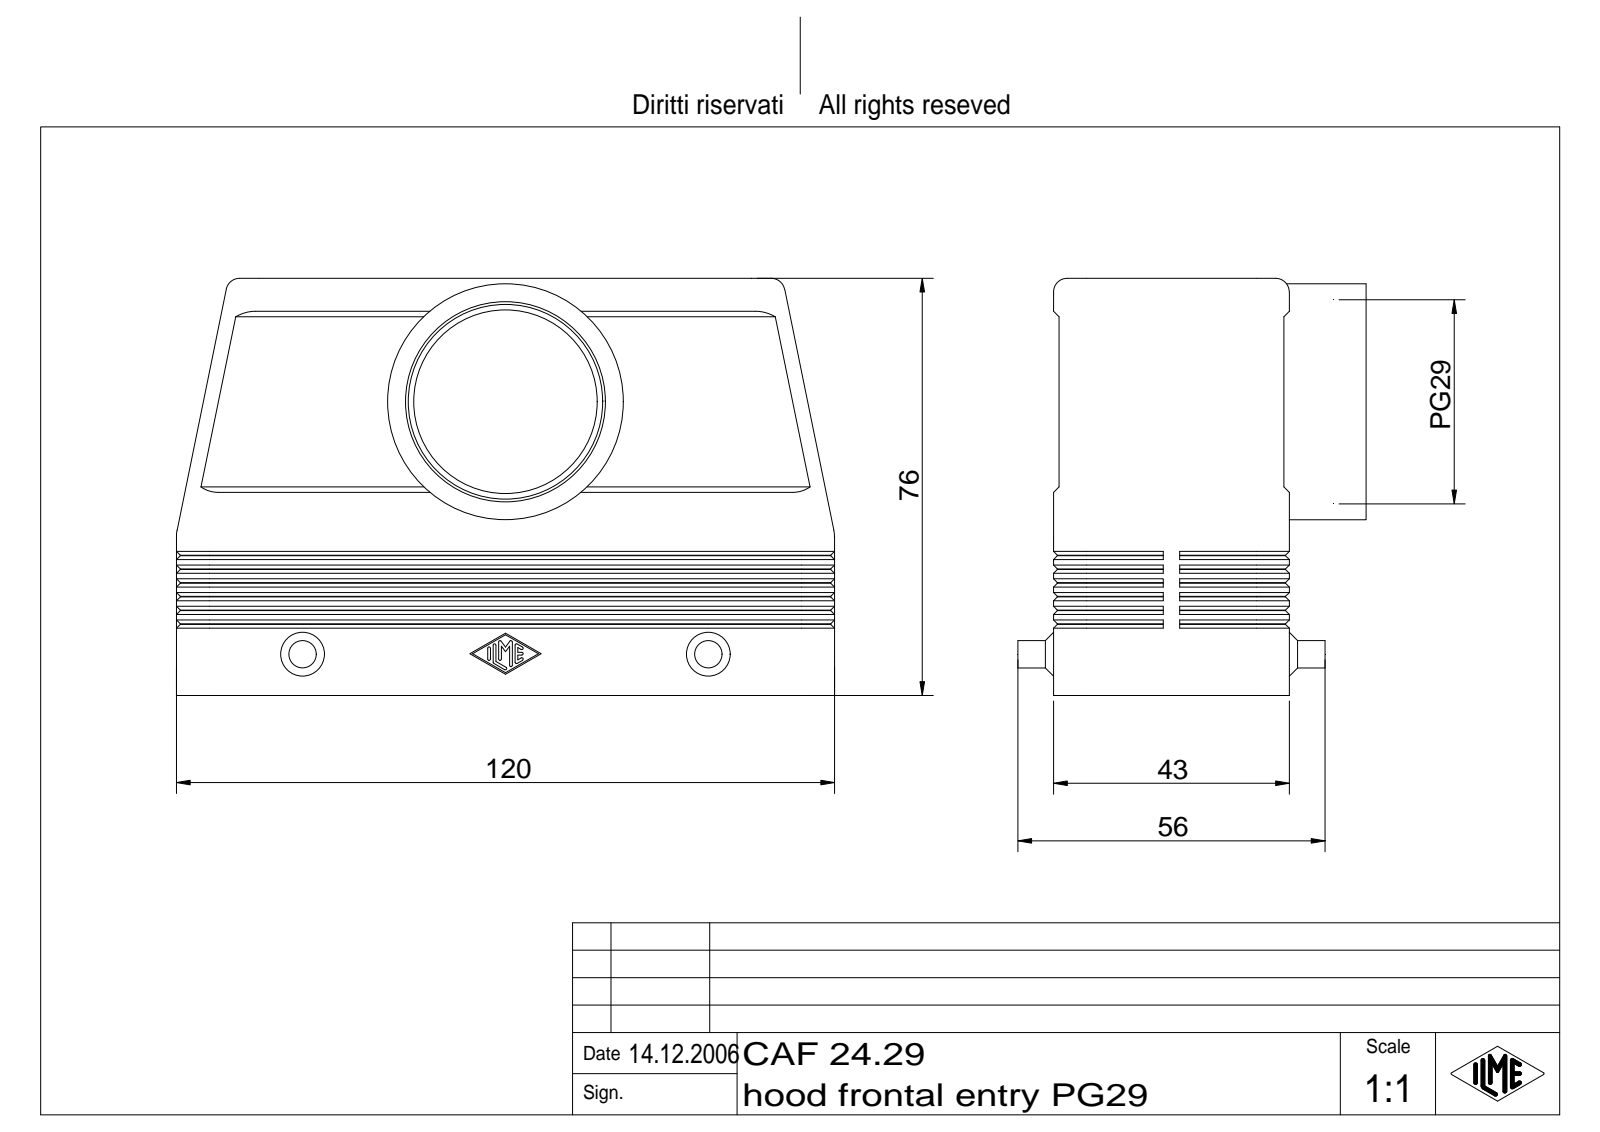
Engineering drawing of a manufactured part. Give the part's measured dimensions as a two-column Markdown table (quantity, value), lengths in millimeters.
| quantity | value |
| --- | --- |
| part name | CAO Tüllengehäuse 2 Bügel für einen Einsatz |
| STEP written by | Autodesk Inventor 7 (AUTOMOTIVE_DESIGN) |
| units | millimeters |
| bodies | 1 solid, 522 faces (200 planar, 128 cylindrical, 194 other) |
| overall size | 120 × 76 × 63.5 |
| volume | 95 224 mm³ |
| surface area | 57 823 mm² |
| round holes (diameter × count) | 33.48 × 1, 35.48 × 1 |
| round bosses / shafts (diameter × count) | 5 × 2, 43 × 1 |
| partial cylindrical surfaces (radius × count) | 0.25 × 14, 6 × 10, 2 × 4, 2.5 × 4, 3 × 4, 5.3 × 2, 23 × 1 |
| main face-to-face distances | 3, 2, 40, 37, 39, 1, 42, 43, 9, 12 |
